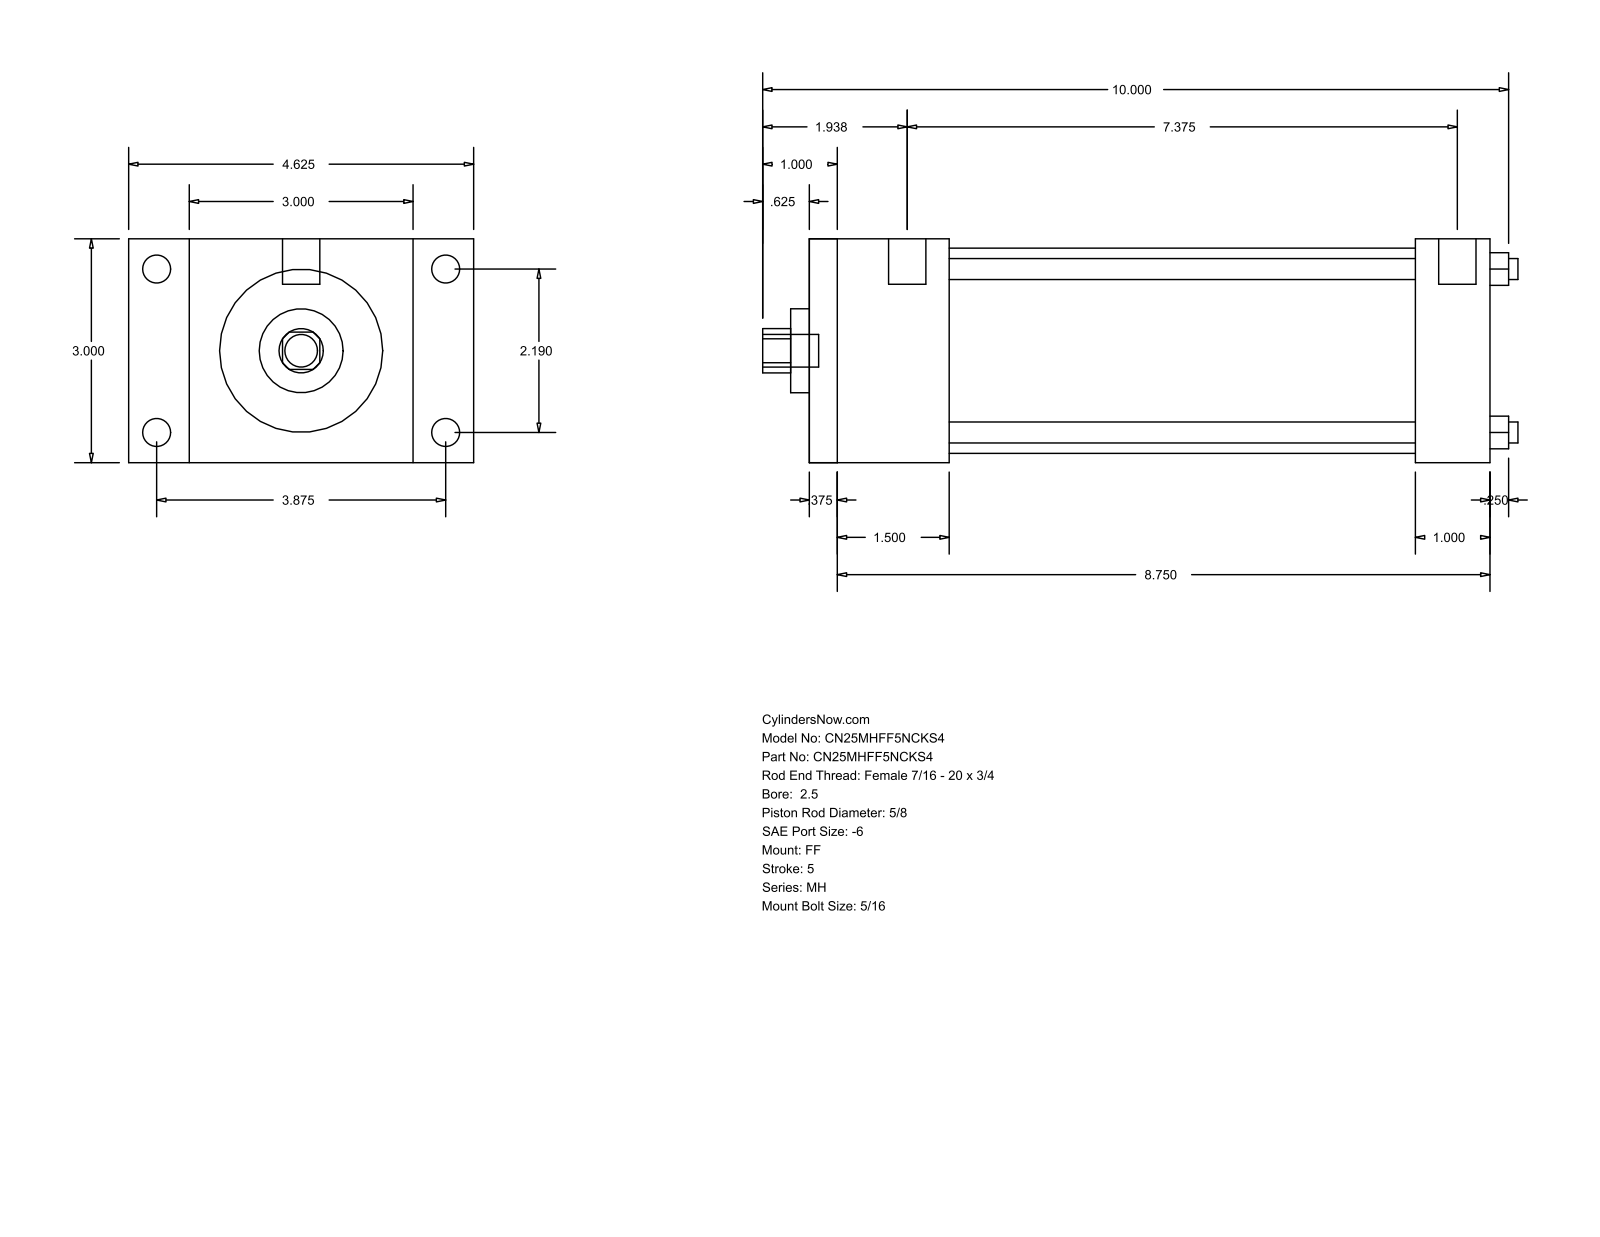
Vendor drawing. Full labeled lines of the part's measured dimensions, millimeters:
Part name (STEP PRODUCT): MH_FF__0250_0.625
STEP written by: GSSL Pune (CONFIG_CONTROL_DESIGN)
Units: millimetres
Bodies: 0 solids, 92 faces (64 planar, 28 cylindrical, 0 other)
Overall size (bounding box): 257.18 × 117.47 × 76.2
Round holes (diameter × count): ⌀7.14 ×4, ⌀15.88 ×1, ⌀28.57 ×1, ⌀69.85 ×1
Round bosses / shafts (diameter × count): ⌀9.53 ×4, ⌀5.56 ×4, ⌀12.7 ×2, ⌀11.11 ×1
Partial cylindrical surfaces — rounded edges, fillets, slot ends (radius × count): R7.54 ×1
Main face-to-face distances: 76.2, 231.77, 9.52, 222.25, 25.4, 47.62, 206.37, 38.1, 196.85, 158.75
Hole centre spacings: 39.33, 55.62, 78.66
